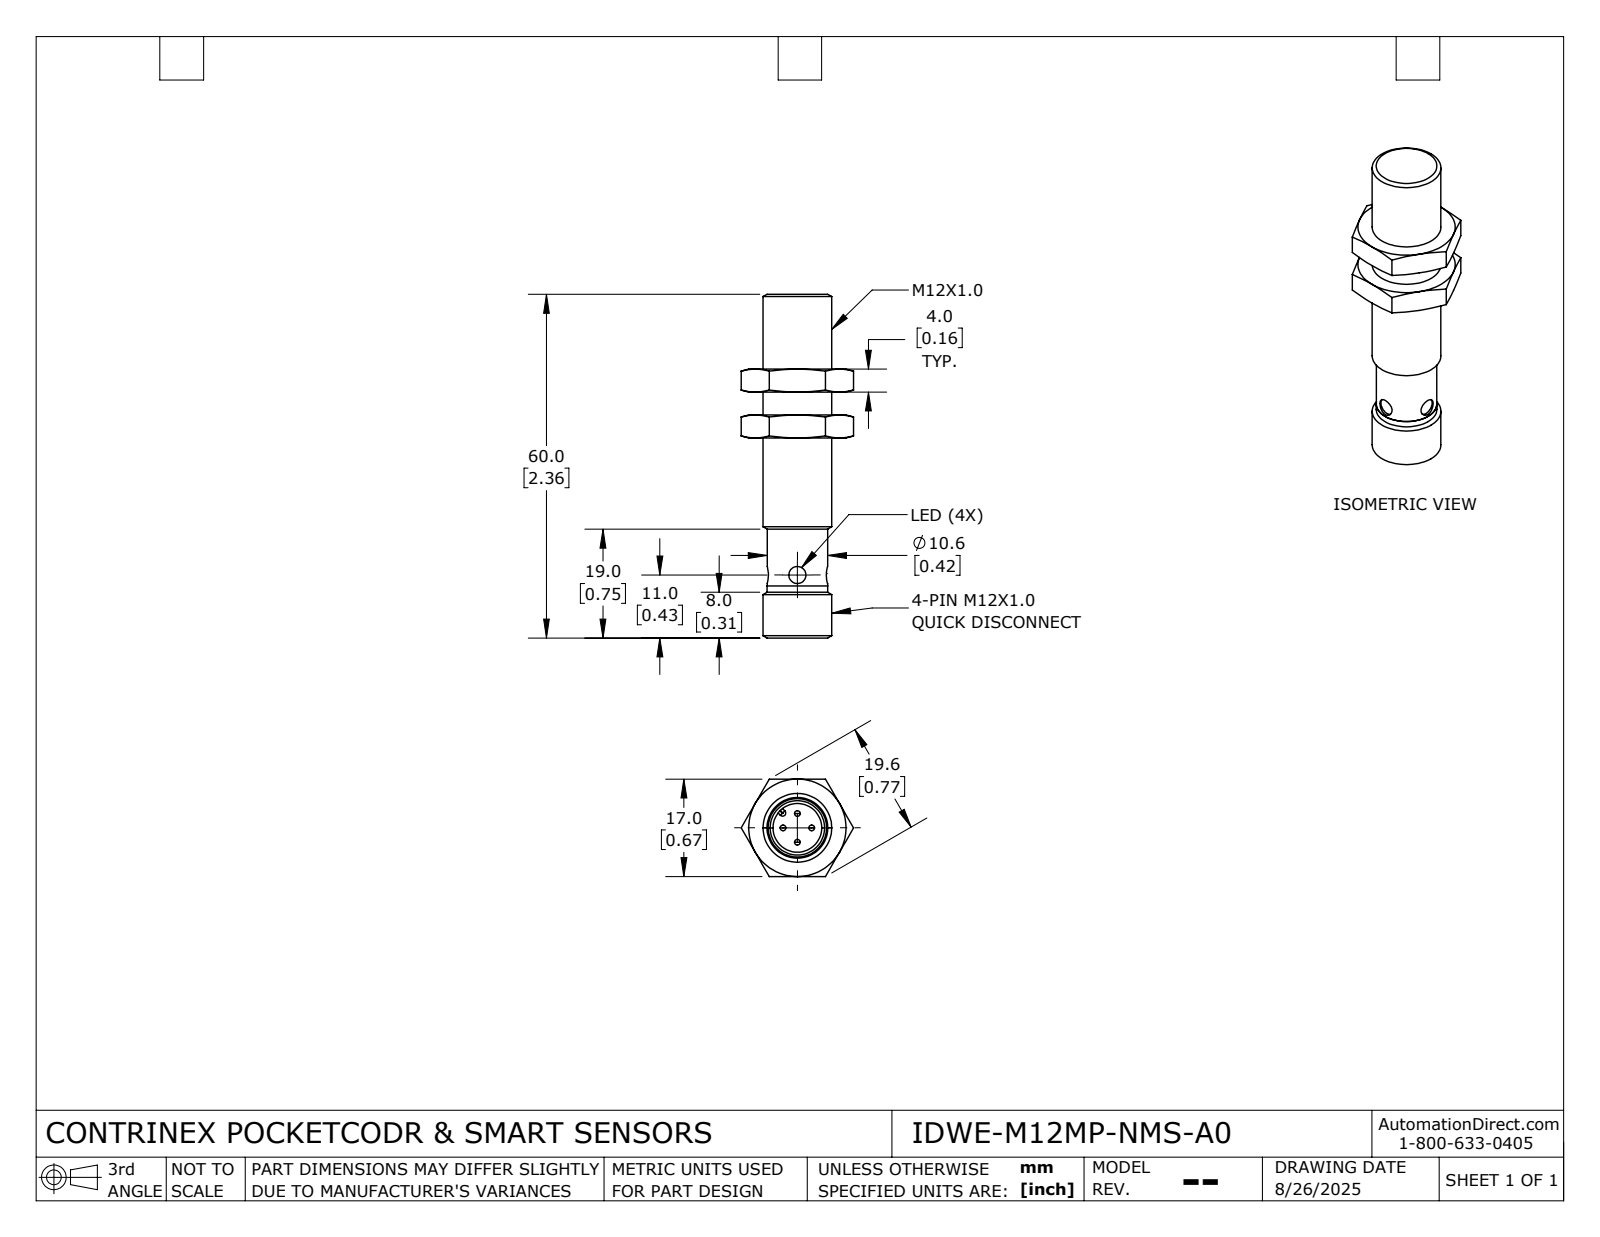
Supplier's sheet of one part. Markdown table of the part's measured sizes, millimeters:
| quantity | value |
| --- | --- |
| part name | IDWE-M12MP-NMS-A0 |
| STEP written by | SolidWorks 2024 (AUTOMOTIVE_DESIGN) |
| units | millimeters |
| bodies | 3 solids, 97 faces (28 planar, 24 cylindrical, 45 other) |
| overall size | 60 × 19.63 × 17 |
| volume | 7 264 mm³ |
| surface area | 4 057 mm² |
| round holes (diameter × count) | 3 × 1, 3 × 1, 8.5 × 1, 10.92 × 1 |
| round bosses / shafts (diameter × count) | 1 × 4, 12 × 1, 10.6 × 1, 10.55 × 1 |
| partial cylindrical surfaces (radius × count) | 0.5 × 2, 0.55 × 1 |
| main face-to-face distances | 4, 8, 17, 12, 13.07, 17.07, 21.07, 25.07, 38.93, 34.93 |
